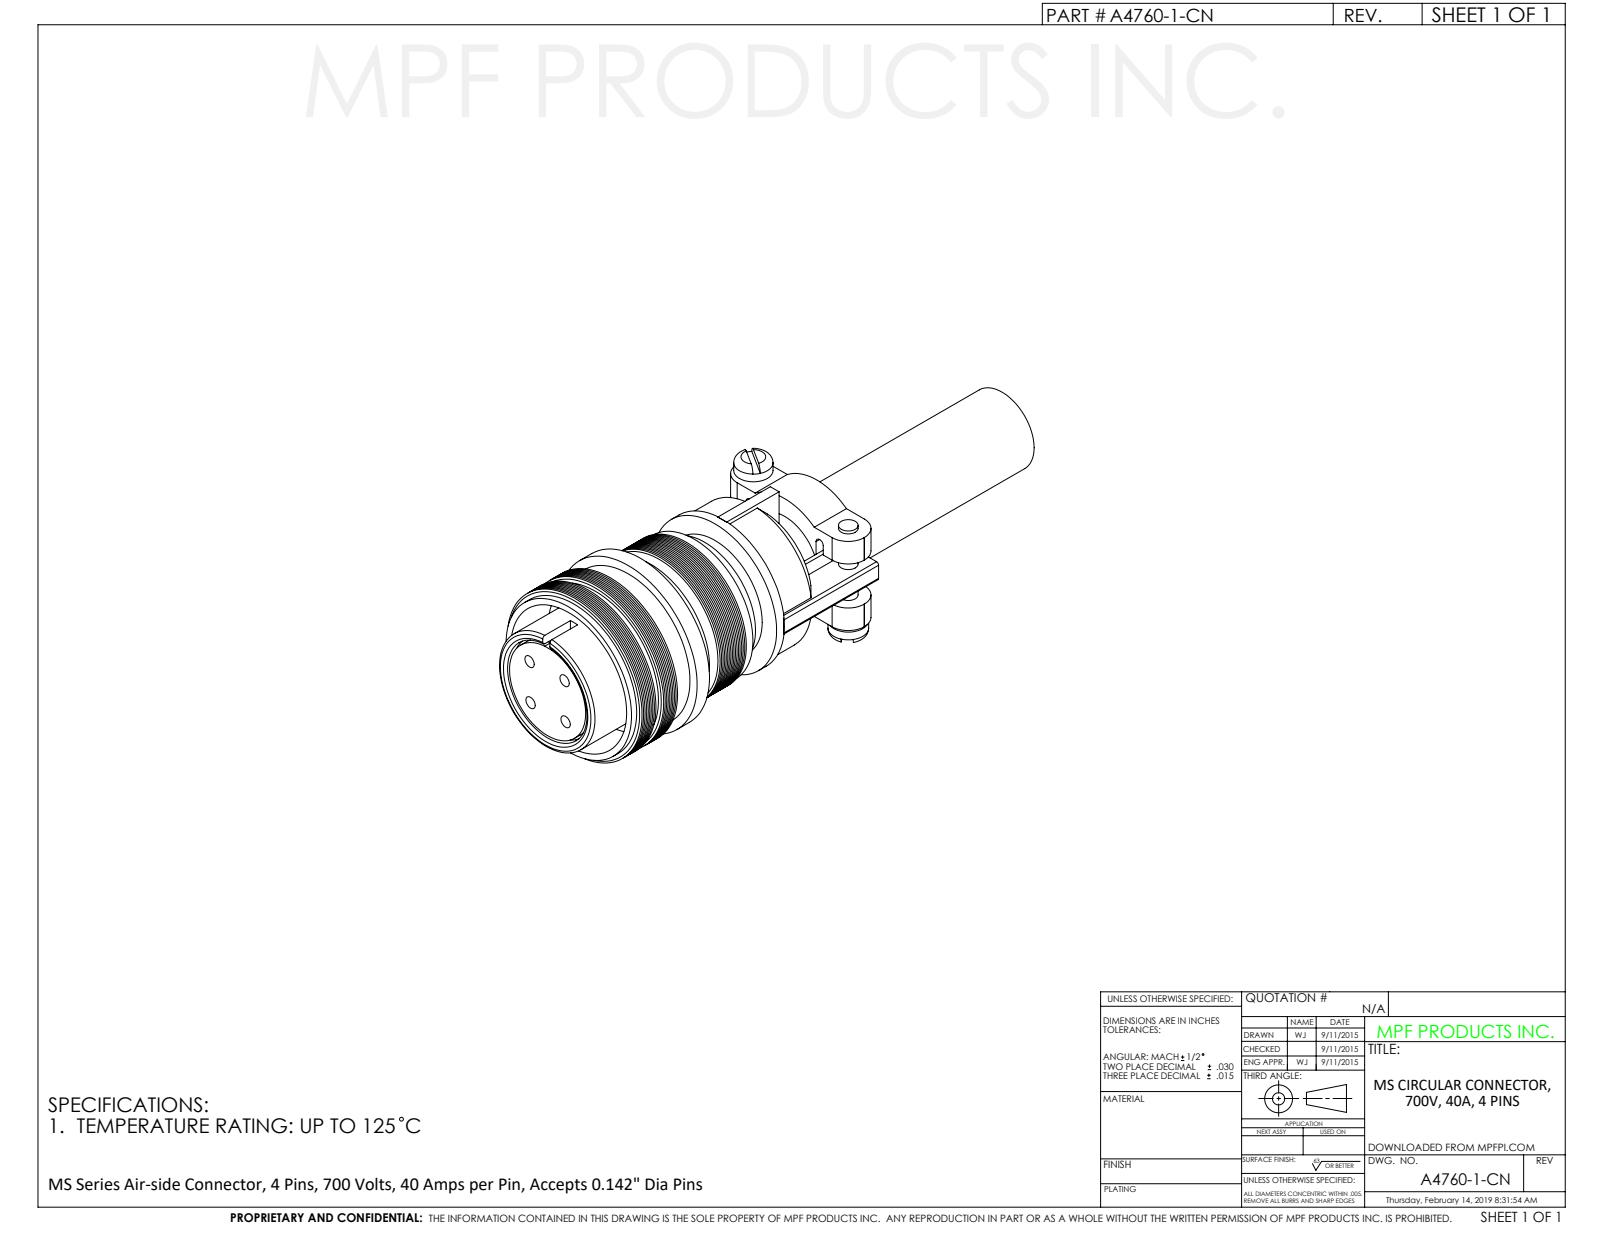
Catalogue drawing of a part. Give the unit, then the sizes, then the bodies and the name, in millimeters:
Units: millimetres
Overall size (bounding box): 112.7 × 34 × 34
Round holes (diameter × count): ⌀2.3 ×4, ⌀14 ×1, ⌀19.8 ×1, ⌀28.6 ×1
Round bosses / shafts (diameter × count): ⌀3.4 ×2, ⌀34 ×1, ⌀31.1 ×1, ⌀31 ×1, ⌀30.5 ×1, ⌀29 ×1, ⌀25.1 ×1, ⌀23.4 ×1
Partial cylindrical surfaces — rounded edges, fillets, slot ends (radius × count): R0.9 ×8, R0.5 ×4, R4 ×4, R8.2 ×1, R12 ×1, R12 ×1
Main face-to-face distances: 30.3, 16.3, 11.9, 18.3, 2.5, 5.1, 53.2, 41.3, 23, 13.3
Hole centre spacings: 6.1, 8.7, 12.2
Volume: 39 200 mm³ · Surface area: 20 320 mm²
Bodies: 1 solid, 377 faces (107 planar, 88 cylindrical, 182 other)
Part name (STEP PRODUCT): A4760-1-CN
STEP written by: SolidWorks 2012 (CONFIG_CONTROL_DESIGN)
